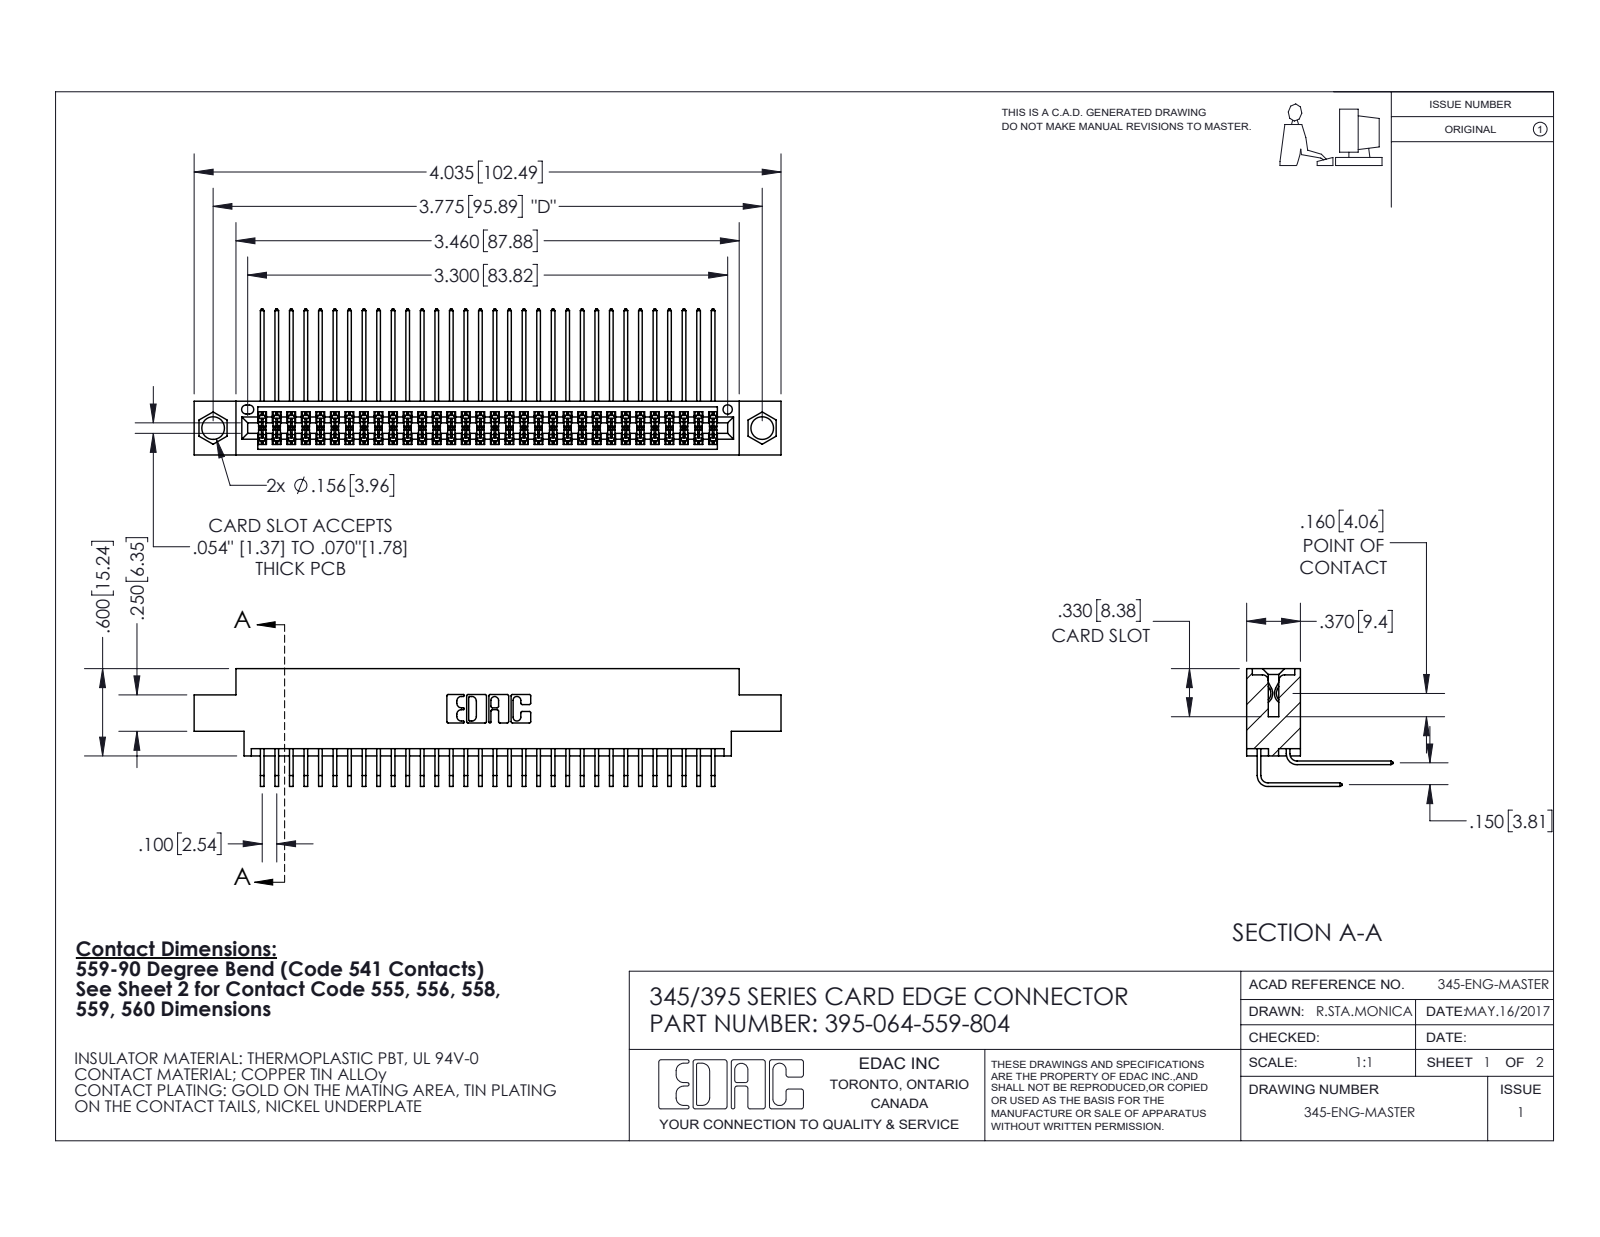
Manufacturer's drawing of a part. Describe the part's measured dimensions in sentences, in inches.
The part is named "395-064-559-804; 345-292-001_558 559 Tail - 1; 345-292-001_559 Tail - 2; 345 Part_0.170 Offset - 0.156 Dia-TI". Its 3-D file was written by "SolidWorks 2020 (CONFIG_CONTROL_DESIGN)". It is 65 solids with 3472 faces: 2338 planar, 1134 cylindrical and 0 other. Overall it measures 4.035 by 1.005 by 0.809 inches. Its volume is 0.611 cubic inches and its surface area 25.32 square inches. Round holes: 2 of diameter 0.156, 1 of diameter 0.064. Partial cylindrical surfaces (rounded edges, fillets, slot ends): 97 of radius 0.006, 22 of radius 0.01, 6 of radius 0.007, 6 of radius 0.031, 3 of radius 0.026, 2 of radius 0.014, 2 of radius 0.019, 2 of radius 0.022. The main face-to-face distances are 0.072, 0.298, 0.37, 0.2, 0.098, 0.272, 0.025, 0.225, 0.175, 0.15. The hole center spacings are 0.27, 3.54, 3.775.
